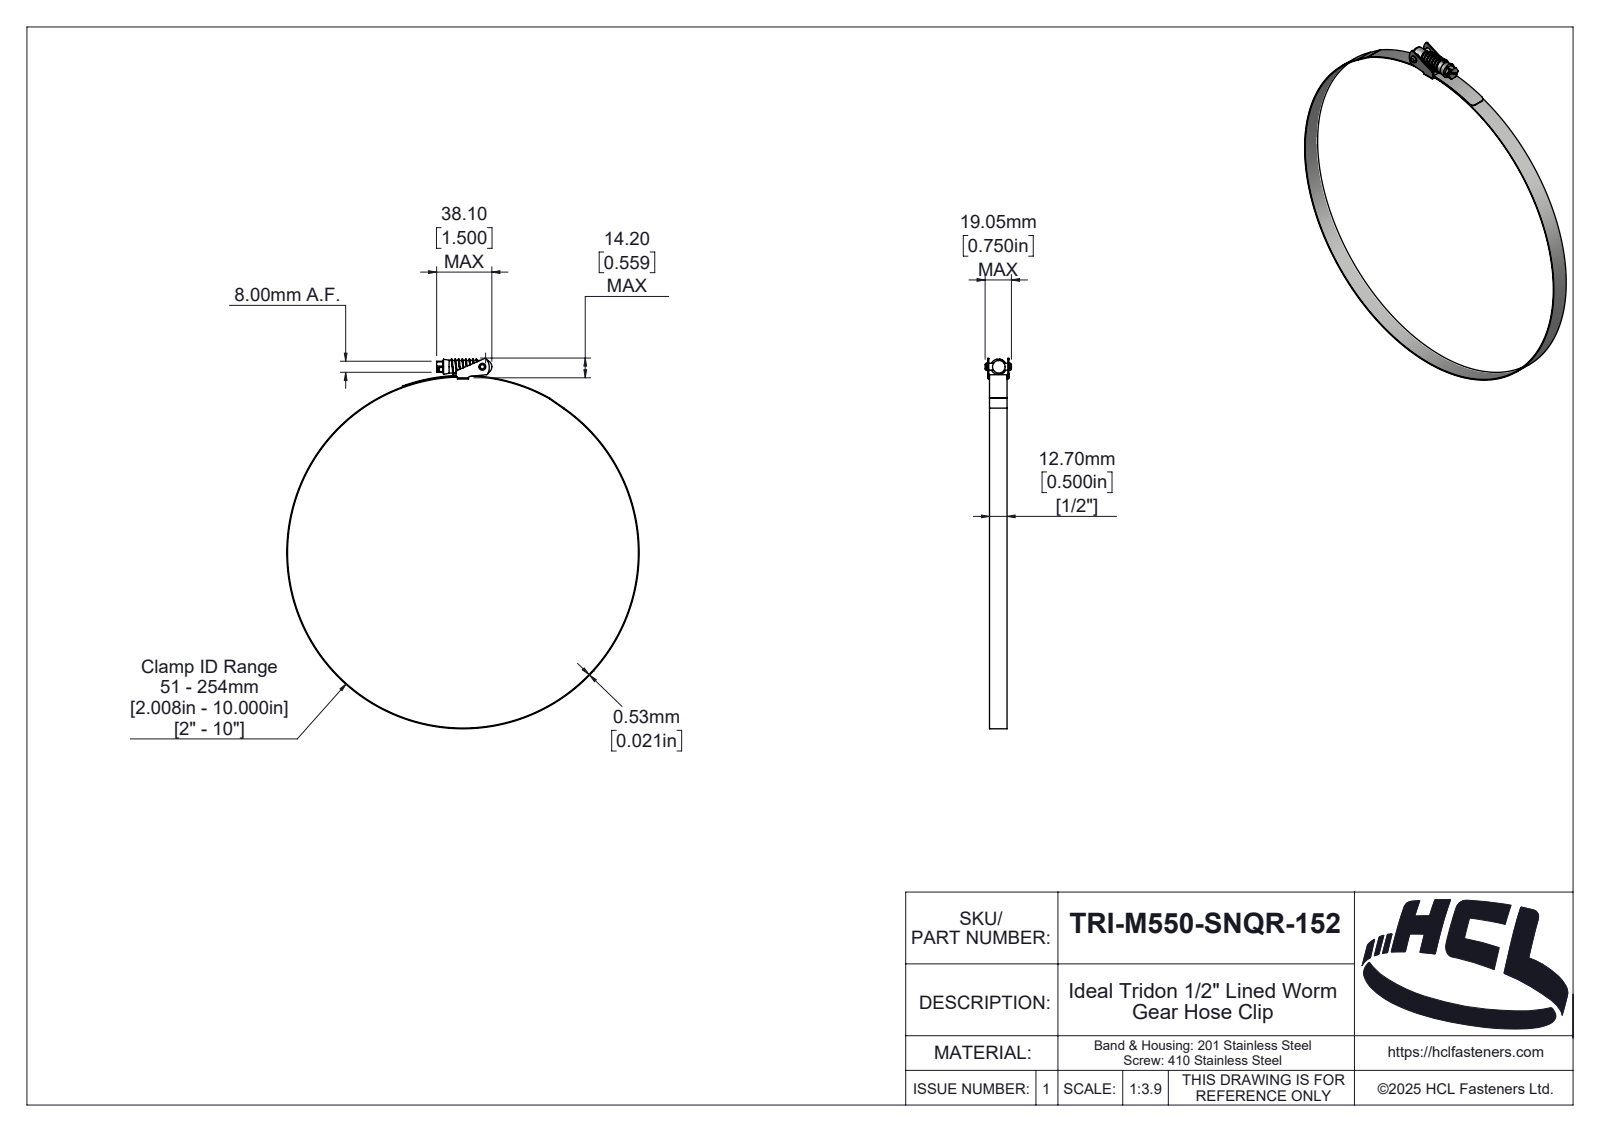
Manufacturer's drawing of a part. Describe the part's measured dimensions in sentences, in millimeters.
The part is named "TRI-M550-SNQR-152". Its 3-D file was written by "SolidWorks 2025 (AUTOMOTIVE_DESIGN)". It is 5 solids with 222 faces: 44 planar, 112 cylindrical and 66 other. Overall it measures 268.02 by 255.06 by 19.05 millimeters. Its volume is 8 863 cubic millimeters and its surface area 25 931 square millimeters. Round holes: 1 of diameter 5, 1 of diameter 254. Round bosses or shafts: 1 of diameter 255.06, 1 of diameter 9.1. Partial cylindrical surfaces (rounded edges, fillets, slot ends): 11 of radius 1, 2 of radius 0.1, 2 of radius 0.9, 2 of radius 3, 1 of radius 0.46, 1 of radius 1.89, 1 of radius 2, 1 of radius 2.35. The main face-to-face distances are 0.8, 12.7, 1.35, 14.05, 14.6, 0.55, 13.25, 15.4, 13.8, 0.53. The hole center spacings are 135.13.
